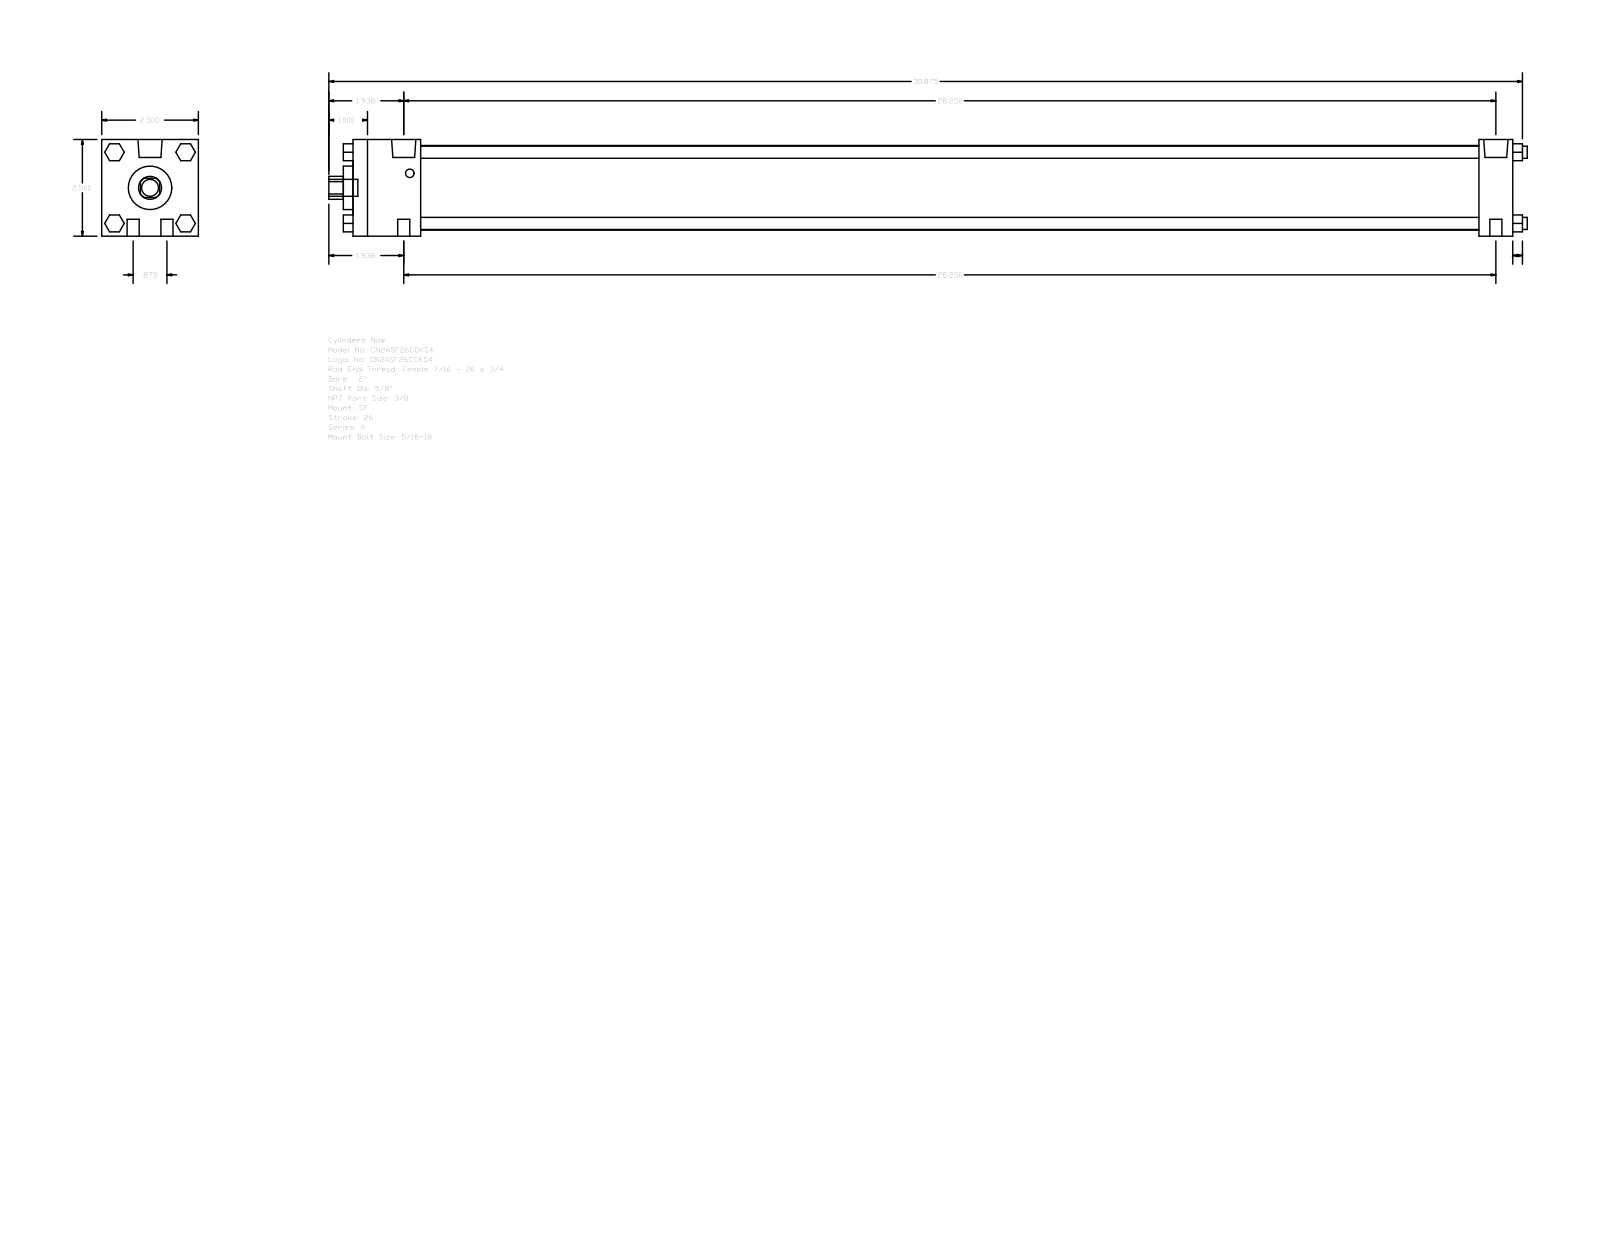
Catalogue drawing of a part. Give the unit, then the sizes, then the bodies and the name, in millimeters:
Units: millimetres
Overall size (bounding box): 787.4 × 63.5 × 63.5
Round holes (diameter × count): ⌀15.88 ×1, ⌀28.57 ×1, ⌀55.63 ×1
Round bosses / shafts (diameter × count): ⌀7.94 ×8, ⌀15.93 ×2, ⌀5.56 ×2, ⌀11.11 ×1
Partial cylindrical surfaces — rounded edges, fillets, slot ends (radius × count): R7.54 ×1
Main face-to-face distances: 63.5, 762, 739.77, 22.23, 44.45, 695.32, 717.55, 768.35, 6.35, 50.8
Bodies: 0 solids, 124 faces (94 planar, 30 cylindrical, 0 other)
Part name (STEP PRODUCT): A_SF__0200_0.625
STEP written by: GSSL Pune (CONFIG_CONTROL_DESIGN)
